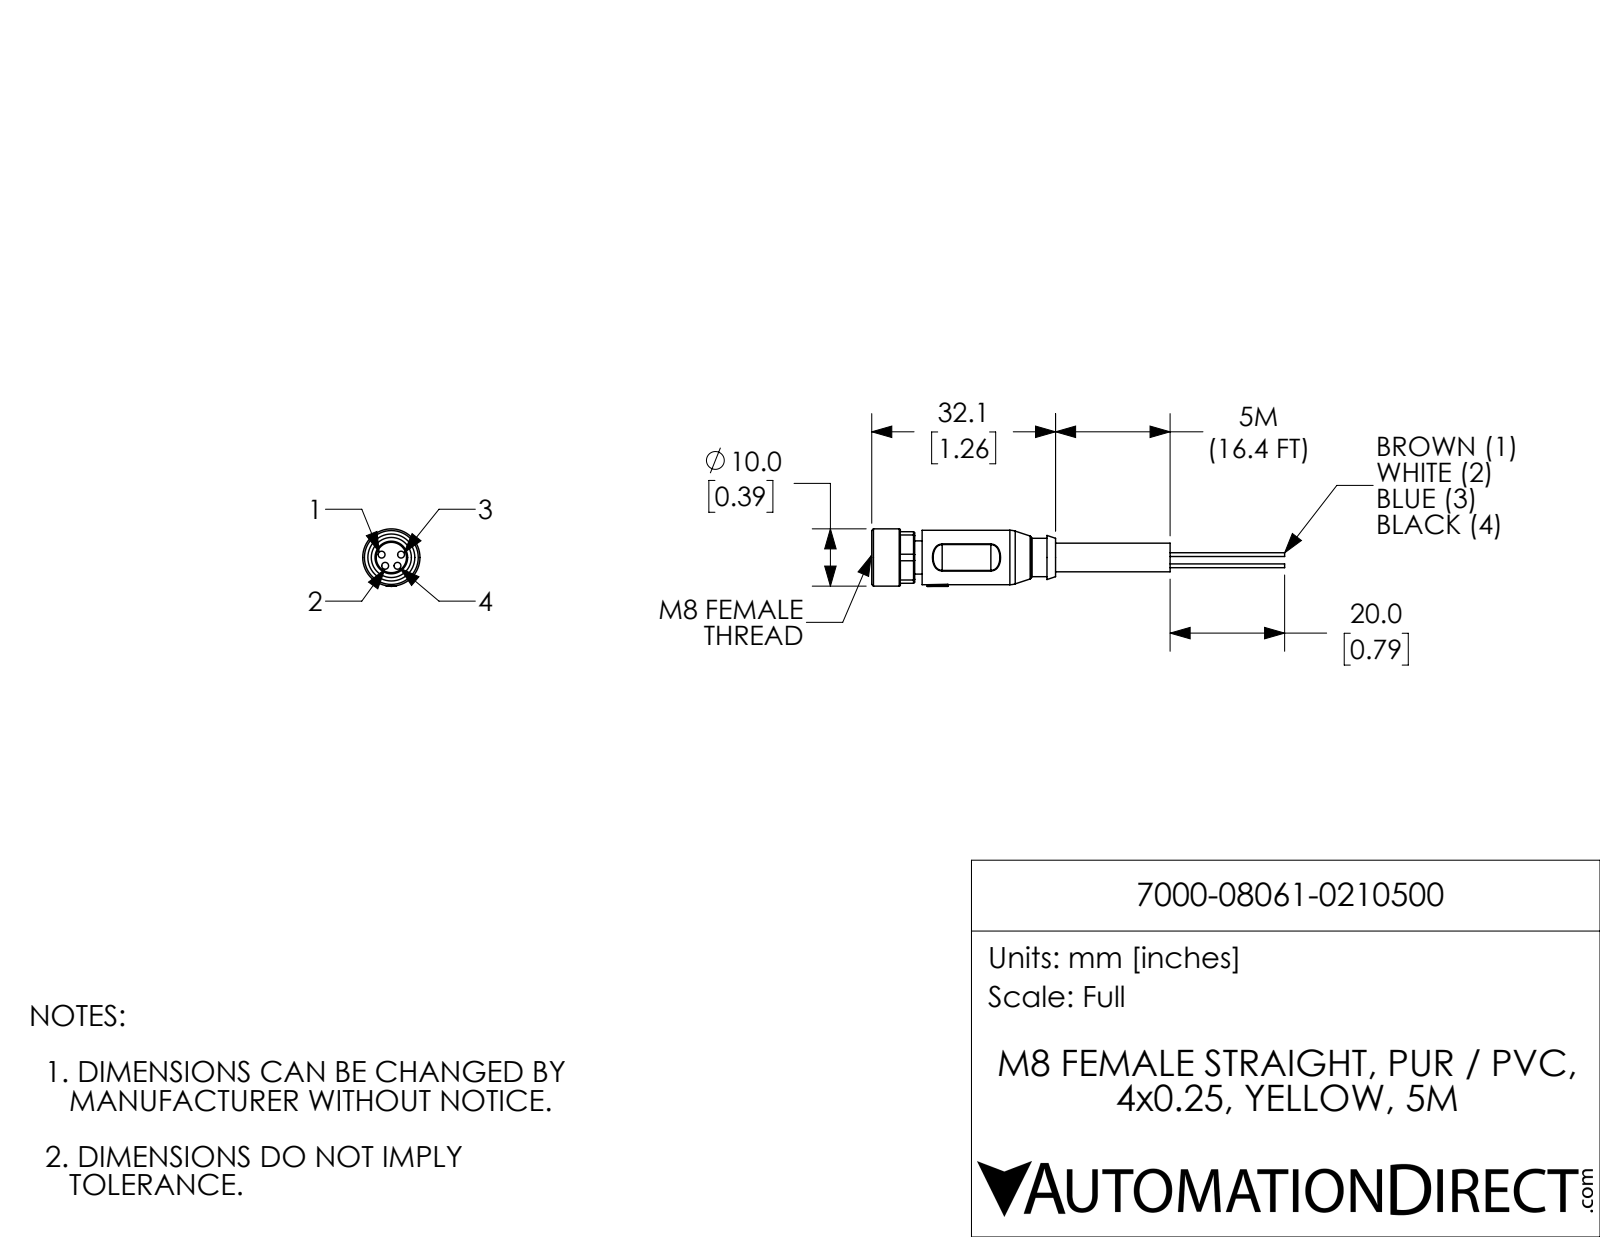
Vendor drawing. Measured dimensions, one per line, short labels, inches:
name: 7000-08061-0210500
written by: SolidWorks 2017 (AUTOMOTIVE_DESIGN)
unit: in
bodies: 1 solid, 115 faces (38 planar, 46 cylindrical, 31 other)
size: 2.839 × 0.396 × 0.394
volume: 0.141 in³; area: 2.944 in²
holes: 4× ⌀0.047, 1× ⌀0.276
bosses: 4× ⌀0.026, 1× ⌀0.394, 1× ⌀0.374, 1× ⌀0.264, 1× ⌀0.228, 1× ⌀0.224, 1× ⌀0.197
rounds: 4× R0.008, 4× R0.098, 1× R0.193, 1× R0.199
face distances: 0.327, 0.051, 0.969, 0.354, 0.059, 0.028, 1.756, 1.705, 0.268, 0.319
hole spacings: 0.07, 0.071, 0.081, 0.133, 0.084, 0.134
